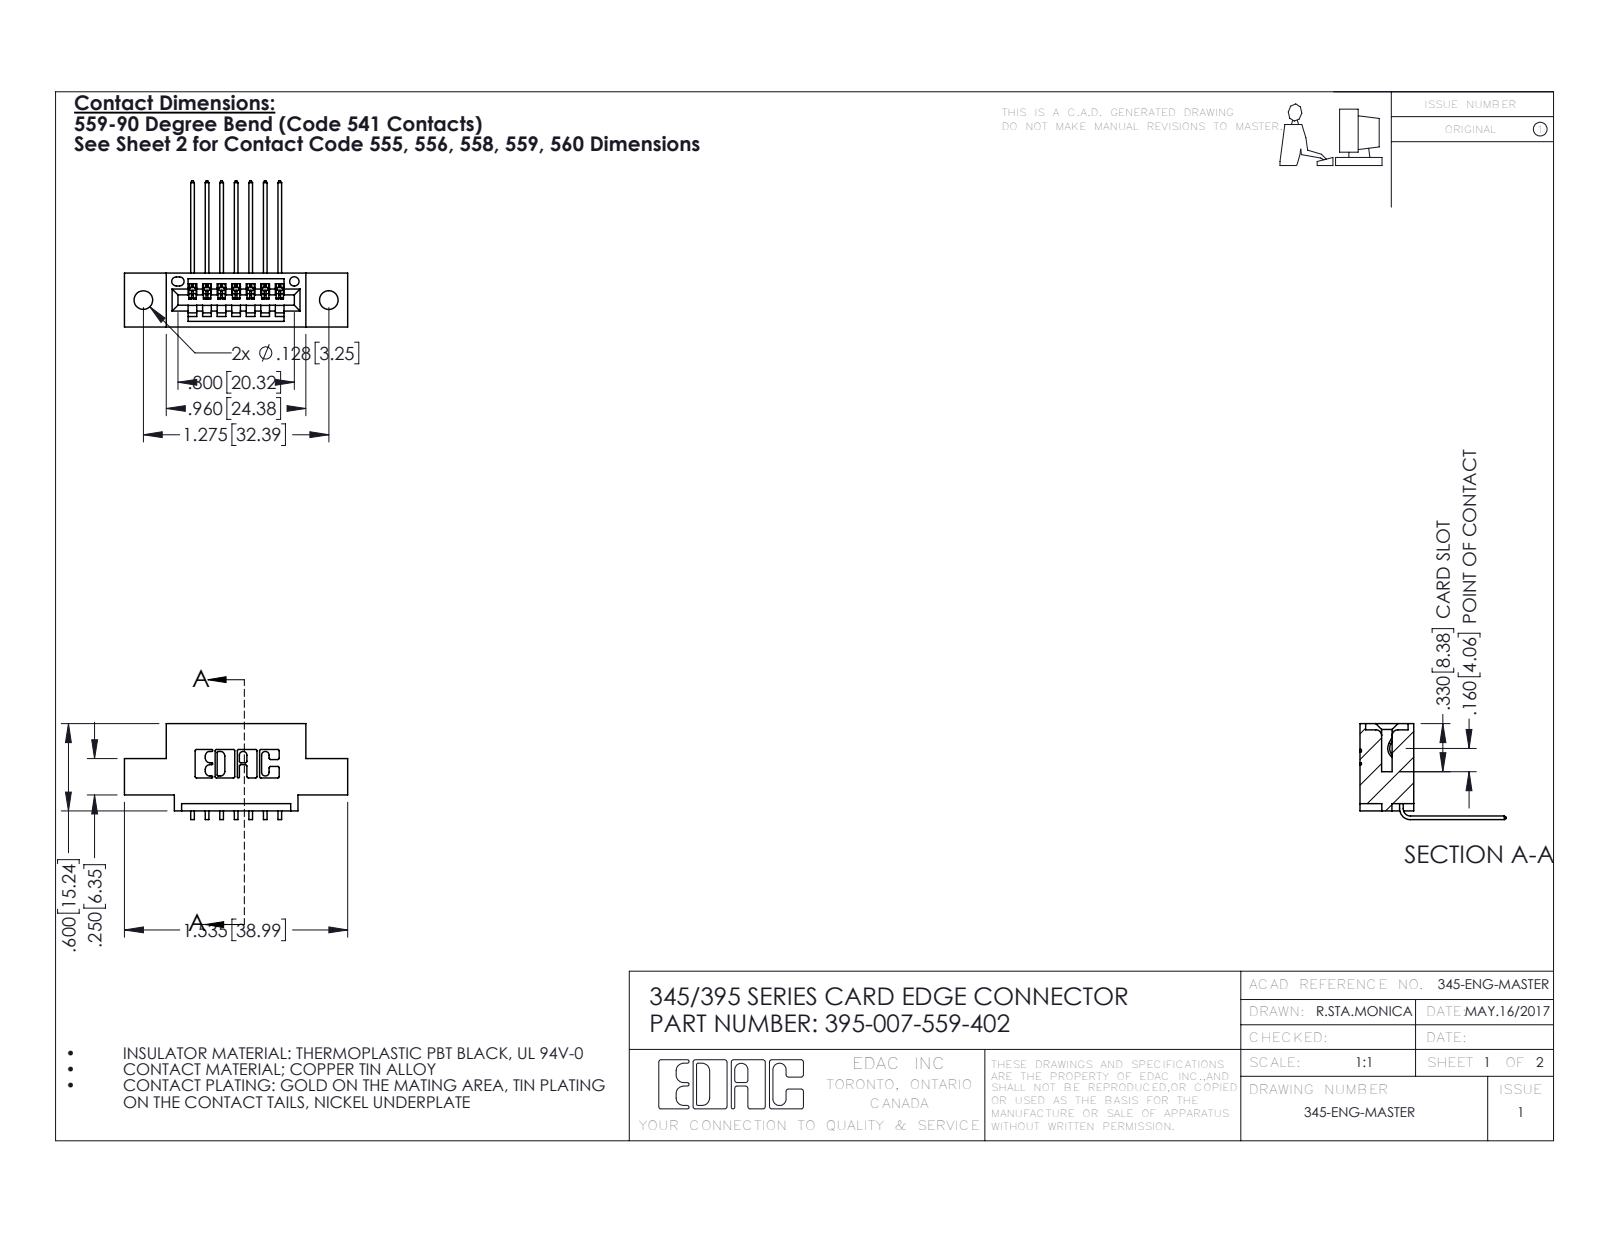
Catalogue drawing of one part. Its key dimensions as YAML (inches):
part_name: "345 Part_0.110 Offset - 0.128 Dia; 345-292-001_558 559 Tail - 1; 395-007-559-402"
step_written_by: "SolidWorks 2016 (CONFIG_CONTROL_DESIGN)"
units: inches
bodies: {solids: 8, faces: 550, planar: 378, cylindrical: 172, other: 0}
overall_size: [1.535, 1.005, 0.659]
volume: 0.203
surface_area: 6.04
round_holes:
  - {diameter: 0.128, count: 2}
  - {diameter: 0.064, count: 1}
partial_cylinders:
  - {radius: 0.01, count: 22}
  - {radius: 0.006, count: 14}
  - {radius: 0.007, count: 6}
  - {radius: 0.031, count: 6}
  - {radius: 0.026, count: 3}
  - {radius: 0.031, count: 2}
  - {radius: 0.04, count: 2}
  - {radius: 0.014, count: 1}
face_to_face_distances: [0.2, 0.37, 0.1, 0.072, 0.298, 0.3, 0.16, 0.06, 0.098, 0.272]
hole_center_spacings: [0.27, 1.045, 1.275]
